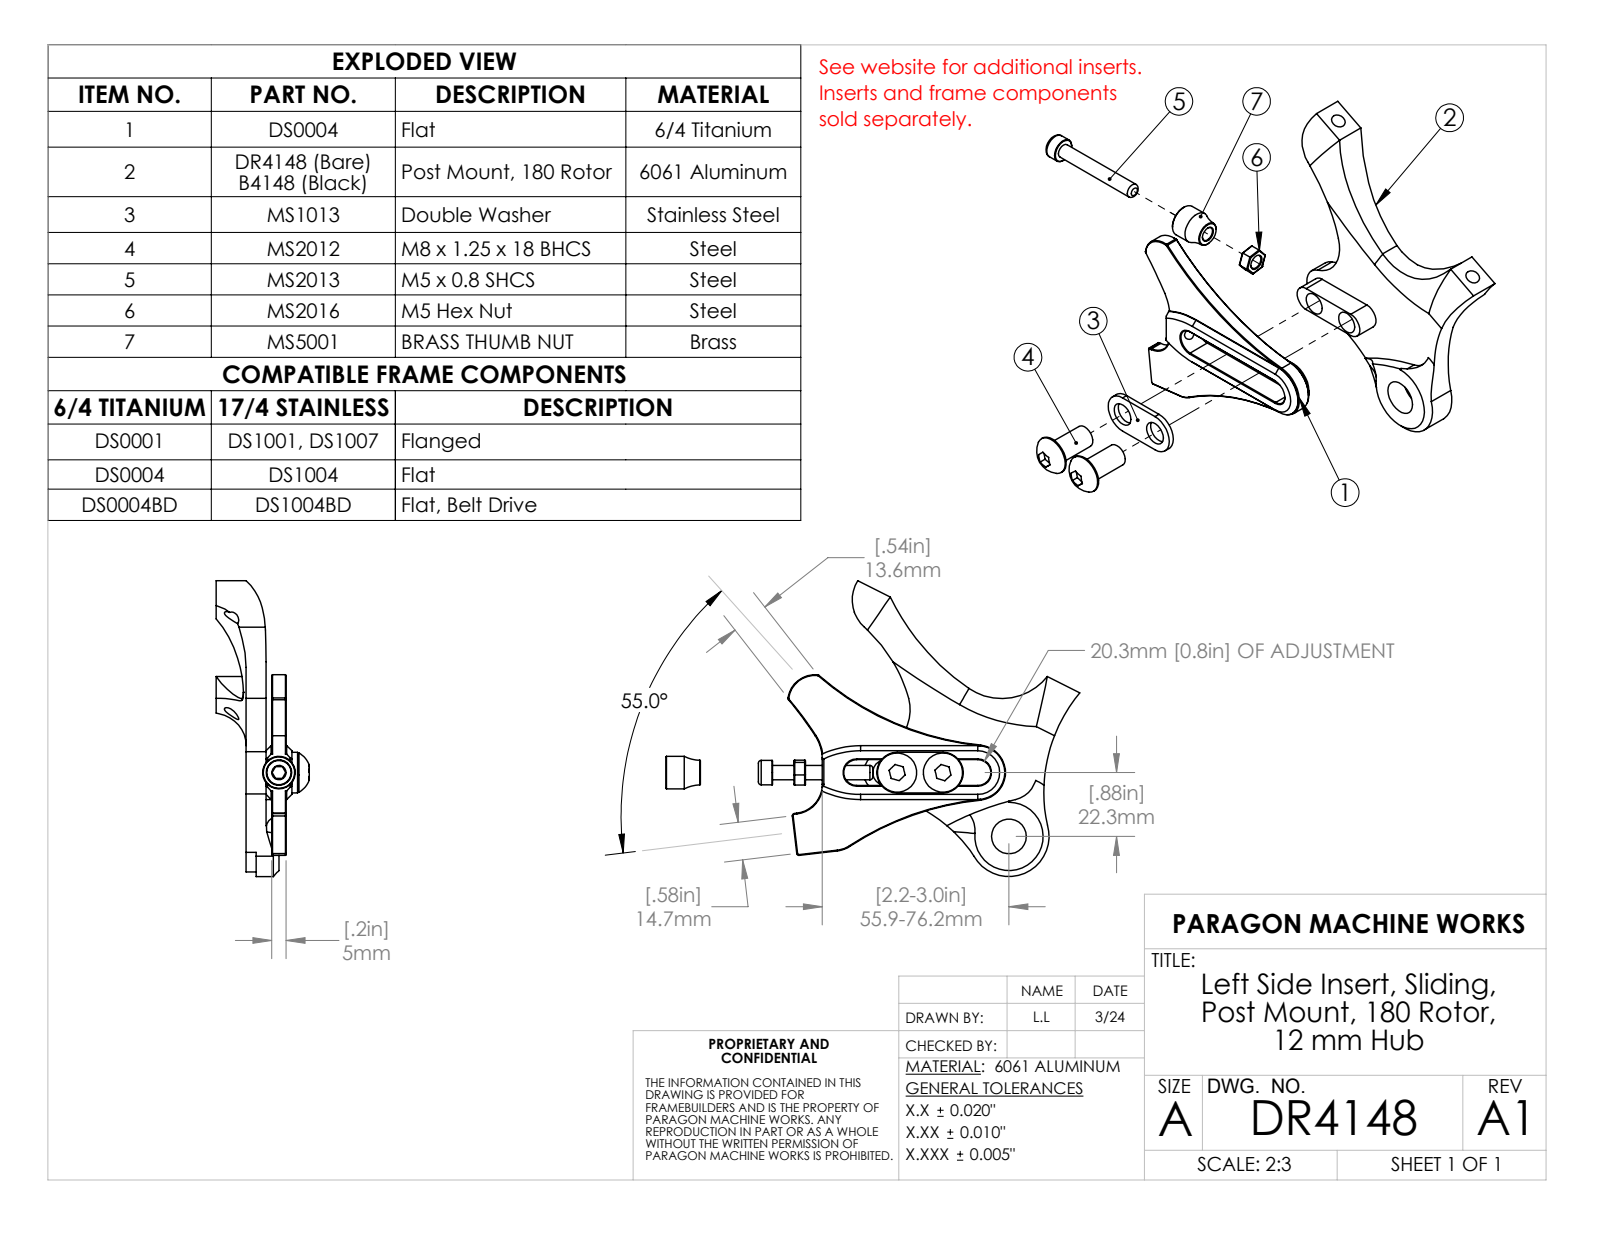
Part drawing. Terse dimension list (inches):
name: DR4148
written by: SolidWorks 2023 (AUTOMOTIVE_DESIGN)
unit: in
bodies: 1 solid, 61 faces (17 planar, 34 cylindrical, 10 other)
size: 4.45 × 3.282 × 1.047
volume: 1.915 in³; area: 20.27 in²
holes: 2× ⌀0.197, 2× ⌀0.312, 1× ⌀0.477
rounds: 2× R0.178, 2× R0.5, 2× R1, 1× R0.3, 1× R0.348, 1× R0.385, 1× R0.394, 1× R0.46
face distances: 0.274, 0.453, 0.179, 0.138, 0.136, 0.315, 0.46, 0.598, 0.734, 0.913
hole spacings: 0.63, 1.262, 1.77, 2.921
